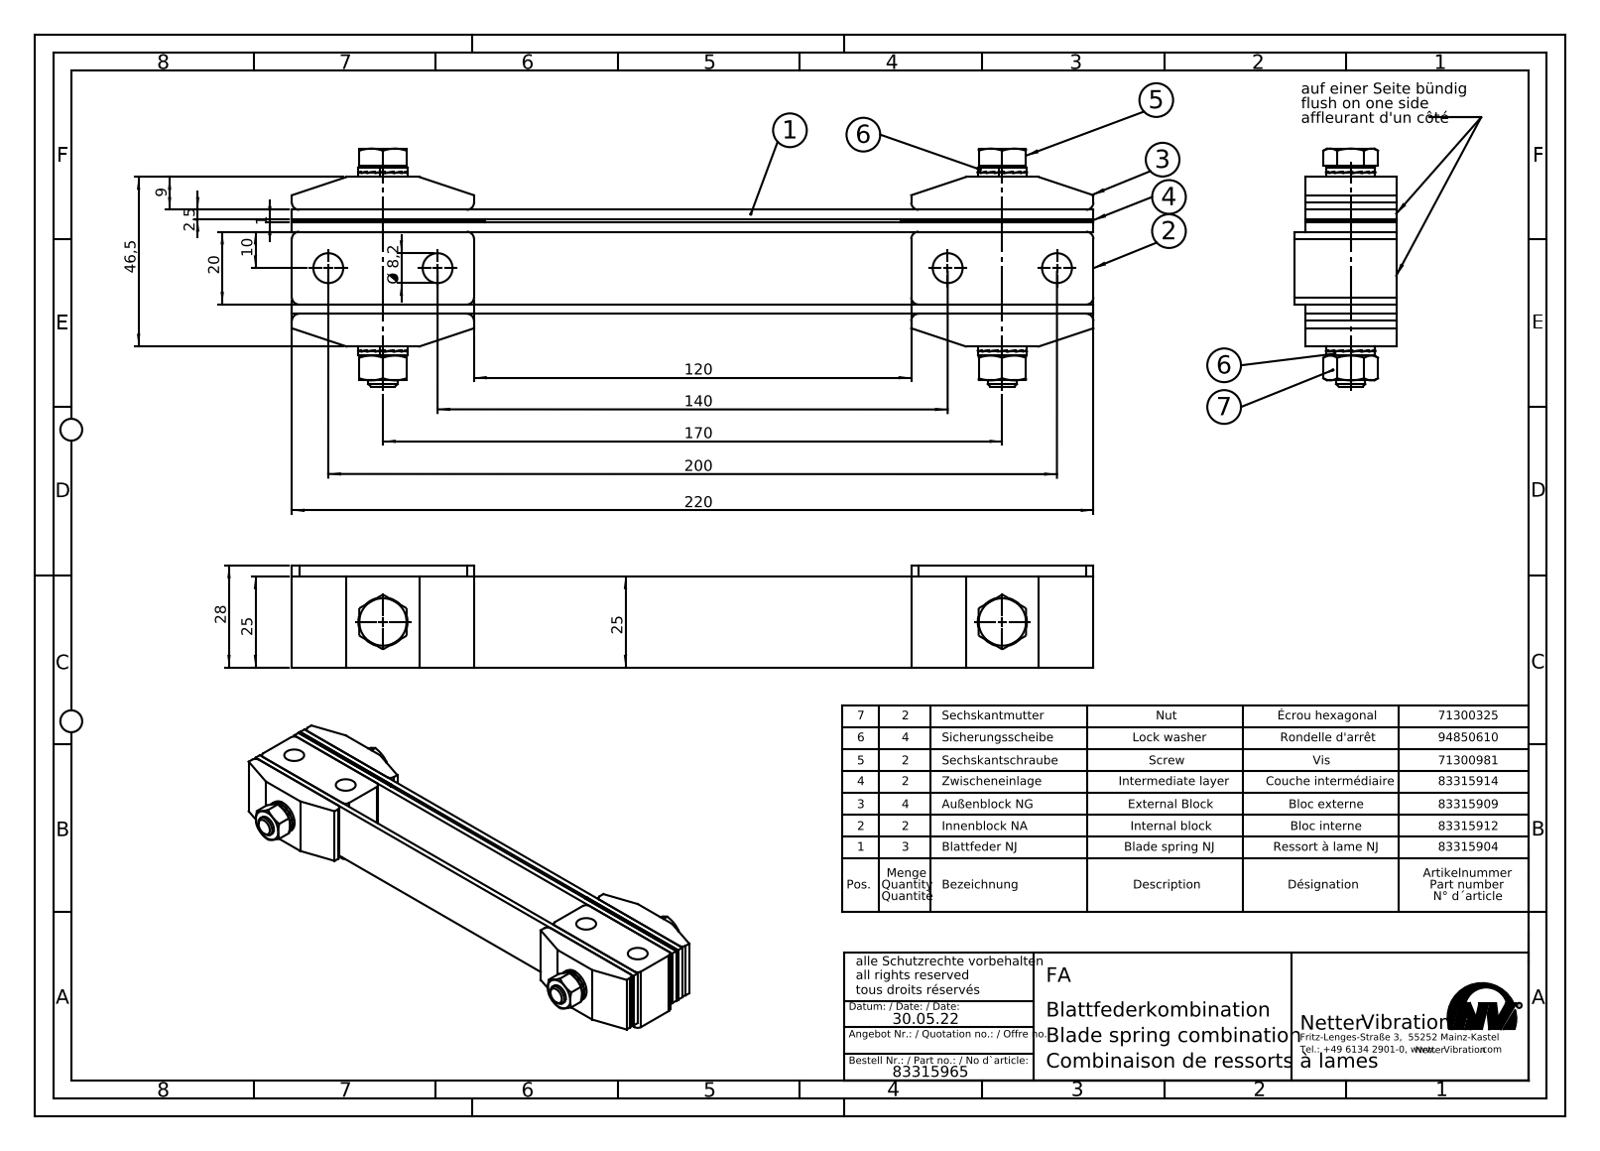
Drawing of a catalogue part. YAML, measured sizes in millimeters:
part_name: "Blattfederkombination FA # 83315965"
step_written_by: "SolidWorks 2015 (AUTOMOTIVE_DESIGN)"
units: millimeters
bodies: {solids: 19, faces: 720, planar: 576, cylindrical: 92, other: 52}
overall_size: [220, 65.3, 28]
volume: 136009
surface_area: 77910
round_holes:
  - {diameter: 8.2, count: 6}
  - {diameter: 6.8, count: 2}
  - {diameter: 8, count: 2}
  - {diameter: 8.5, count: 2}
  - {diameter: 8.7, count: 2}
round_bosses_or_shafts:
  - {diameter: 13.5, count: 2}
  - {diameter: 13, count: 2}
partial_cylinders:
  - {radius: 2, count: 16}
face_to_face_distances: [2.5, 22.5, 3.5, 26, 25, 1, 20, 23.5, 6, 28.5]
hole_center_spacings: [170, 30, 140, 200]
